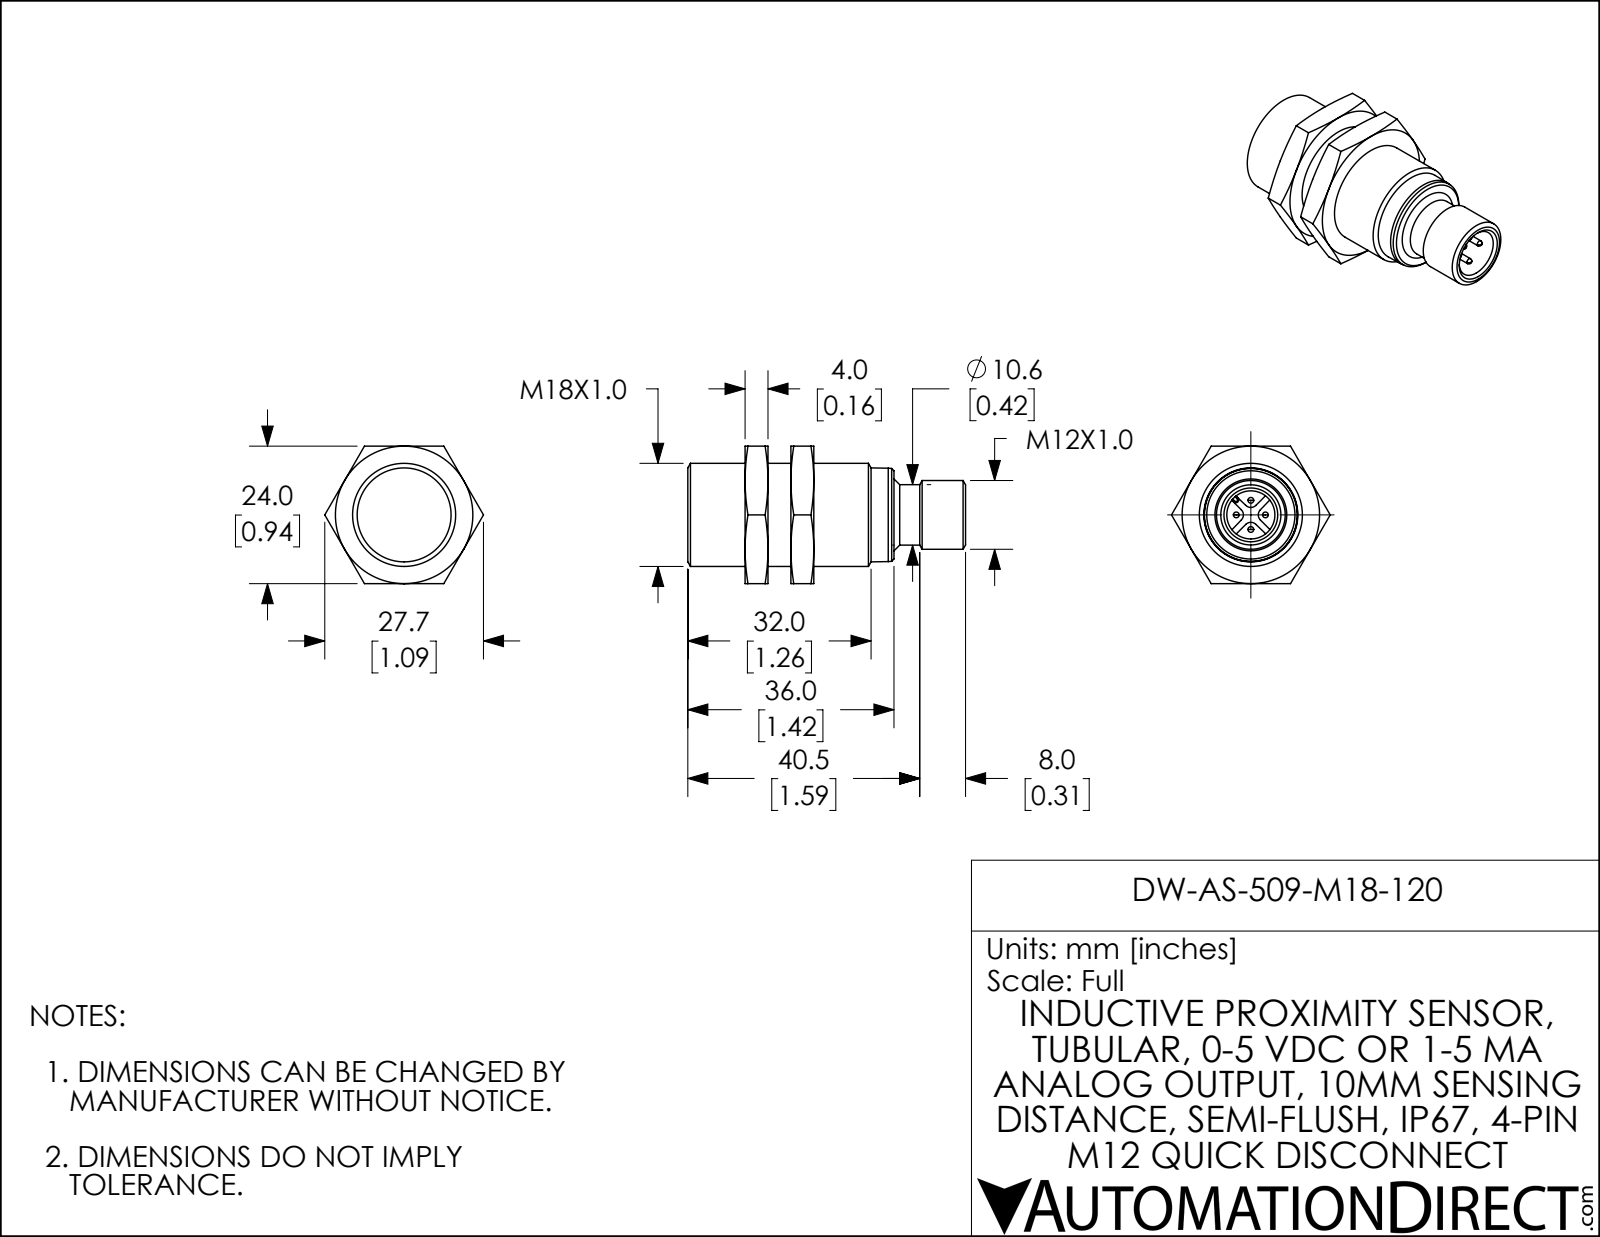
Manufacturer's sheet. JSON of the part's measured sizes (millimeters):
{"part_name": "DW-AS-509-M18-x20", "step_written_by": "SolidWorks 2018 (AUTOMOTIVE_DESIGN)", "units": "millimeters", "bodies": {"solids": 1, "faces": 55, "planar": 21, "cylindrical": 15, "other": 19}, "overall_size": [48.5, 18, 18], "volume_mm3": 4473, "surface_area_mm2": 5041, "round_holes": [[8.4, 1]], "round_bosses_or_shafts": [[1, 4], [18, 1], [12, 1], [10.55, 1]], "partial_cylinders_radius": [[1.25, 4], [0.2, 2], [0.5, 1]], "face_to_face_distances": [1.4, 30.06, 28.66, 36, 34.6, 5.94, 39.5, 38.1, 9.44, 3.5]}
